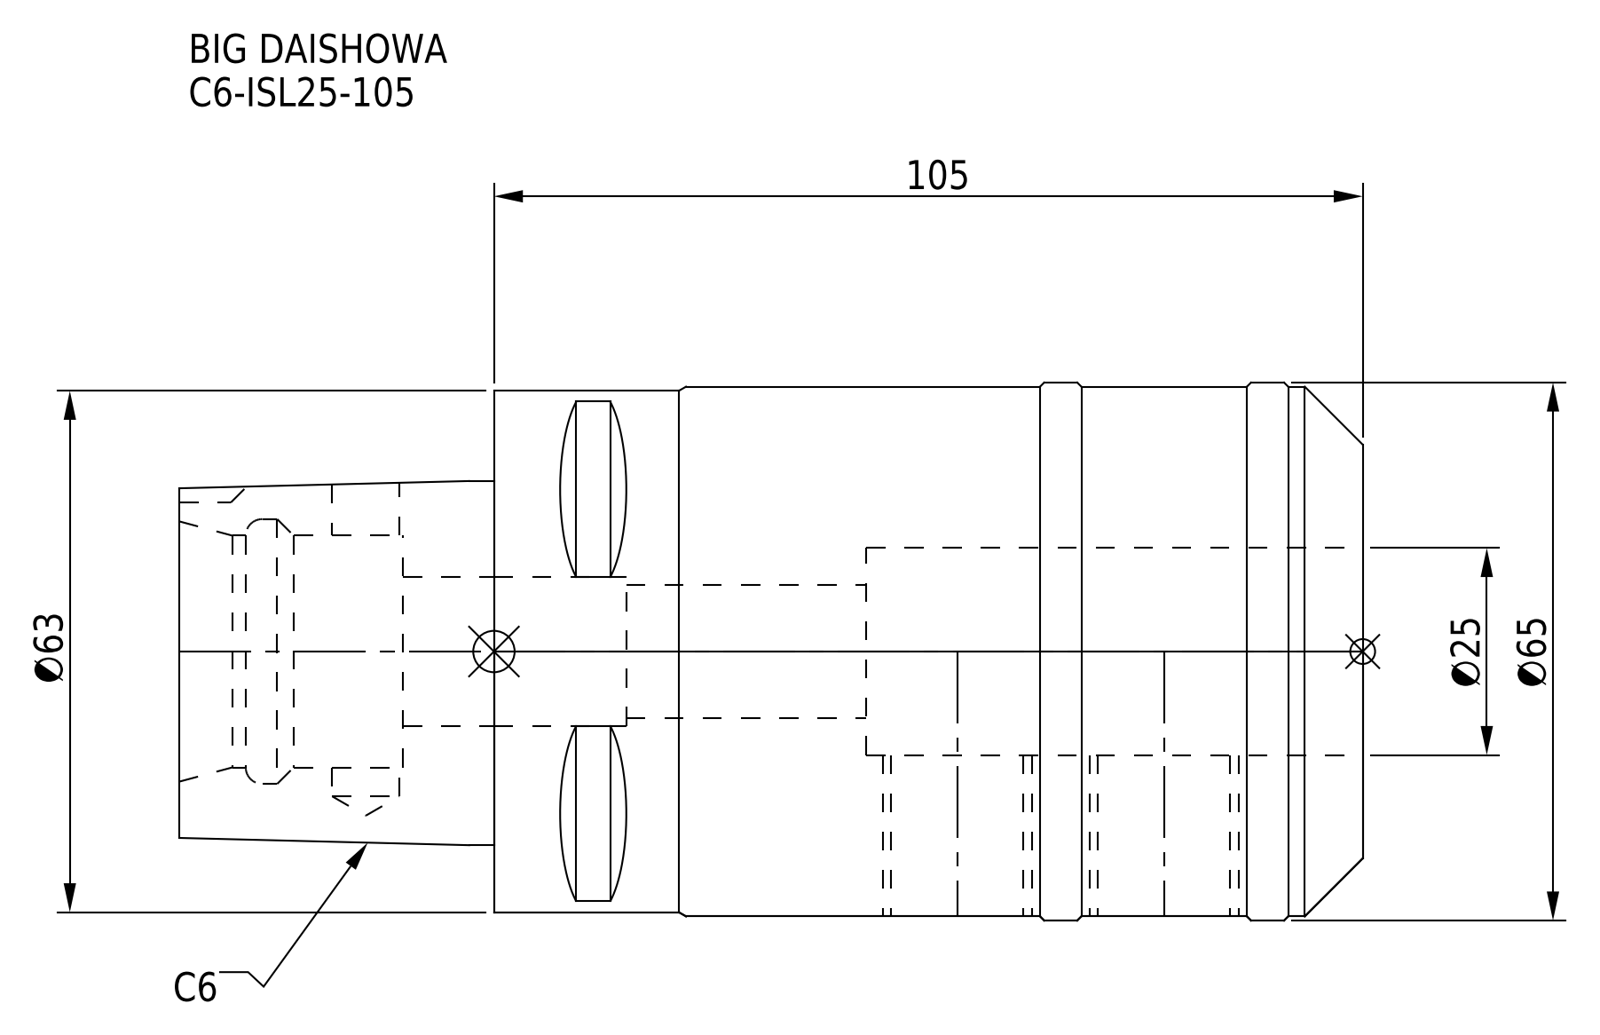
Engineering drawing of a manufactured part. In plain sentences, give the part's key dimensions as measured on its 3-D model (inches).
The part is named "C6-ISL25-105". Its 3-D file was written by "CREO PARAMETRIC BY PTC INC, 2016380 (AUTOMOTIVE_DESIGN)". It is 1 solid with 79 faces: 28 planar, 29 cylindrical and 22 other. Overall it measures 5.63 by 2.559 by 2.559 inches. Its volume is 19.81 cubic inches and its surface area 65.16 square inches. Round holes: 1 of diameter 0.319, 1 of diameter 0.63, 1 of diameter 0.709, 1 of diameter 0.984, 1 of diameter 1.102, 1 of diameter 1.26. Round bosses or shafts: 1 of diameter 2.559, 1 of diameter 2.52, 1 of diameter 2.48. Partial cylindrical surfaces (rounded edges, fillets, slot ends): 1 of radius 0.197. The main face-to-face distances are 4.134, 5.63, 1.496, 1.063, 4.567, 0.433, 2.362, 1.772, 2.205, 3.268.
